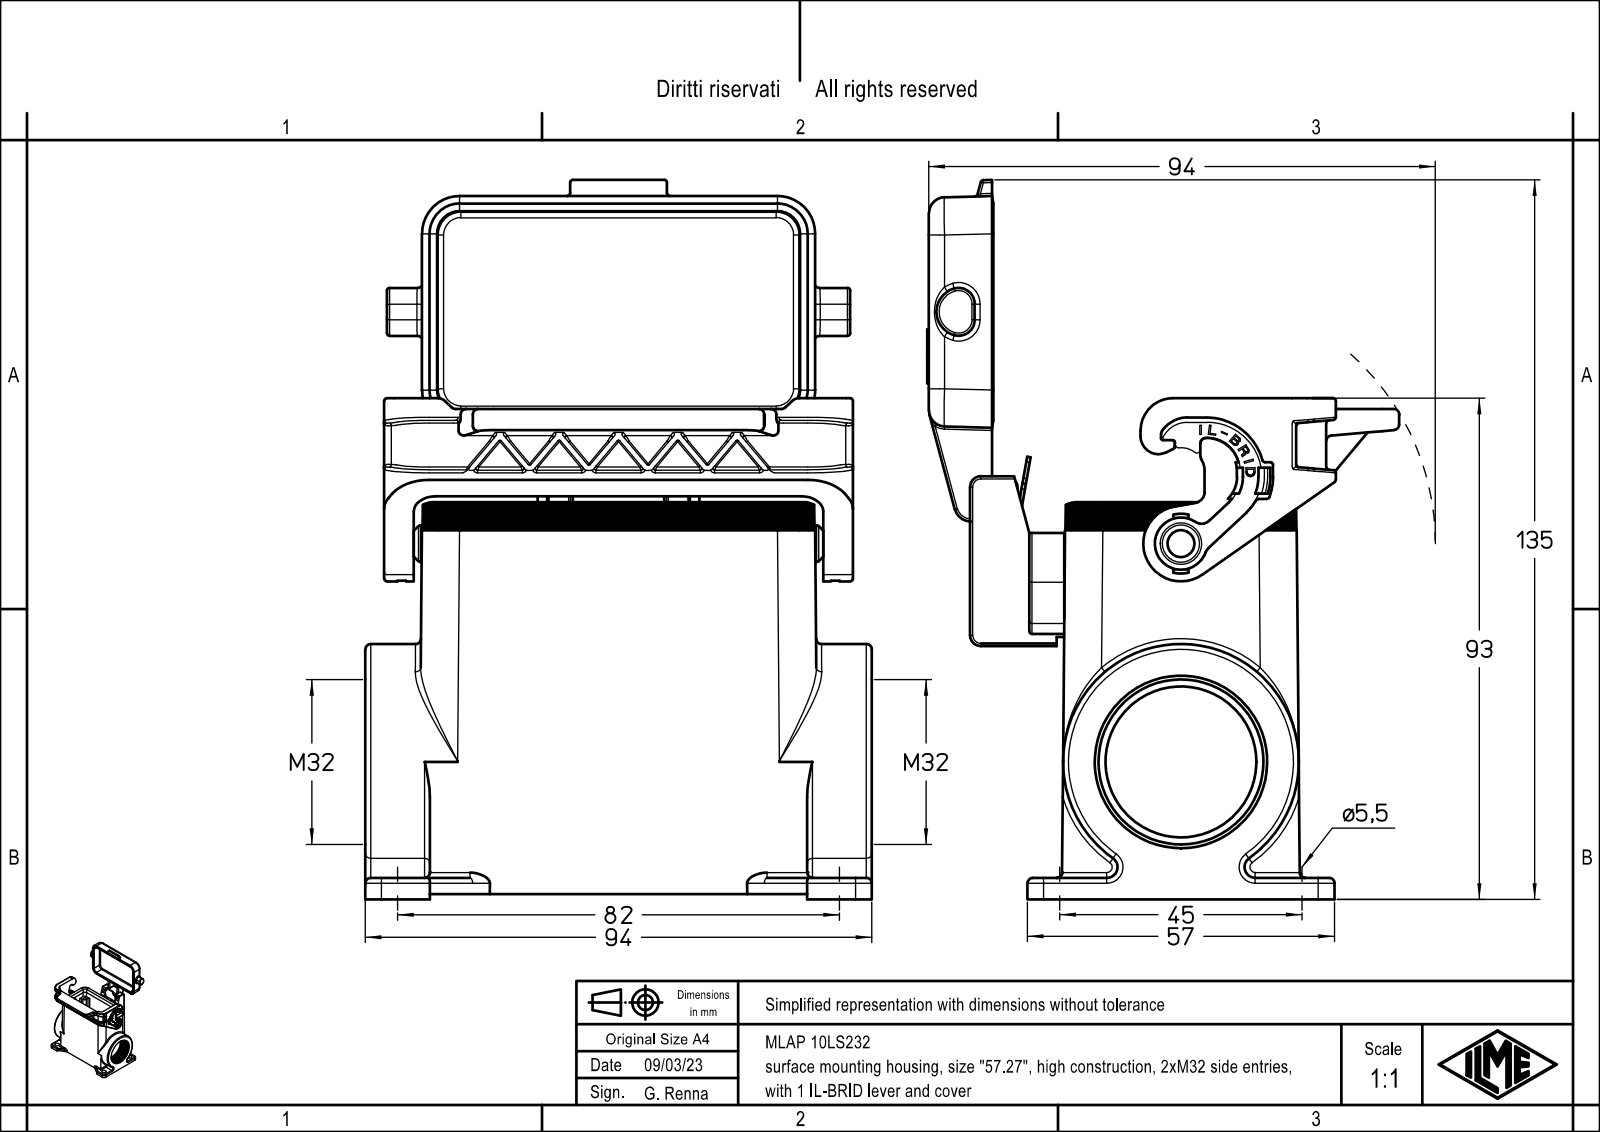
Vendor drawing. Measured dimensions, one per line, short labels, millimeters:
name: MLAP 10LS232
written by: Creo Elements/Direct Modeling 20.1B 02-Apr-2019 (C) Parametric Technology GmbH (AUTOMOTIVE_DESIGN)
unit: mm
bodies: 1 solid, 1402 faces (804 planar, 399 cylindrical, 199 other)
size: 133.49 × 94 × 87.8
volume: 135 244 mm³; area: 72 816 mm²
holes: 4× ⌀3, 4× ⌀3.5, 4× ⌀5.5, 1× ⌀3.25, 1× ⌀5.4, 1× ⌀7.7, 1× ⌀28, 1× ⌀30.6
bosses: 1× ⌀43.75, 1× ⌀8.4, 1× ⌀6.9, 1× ⌀6.8, 1× ⌀5.2, 1× ⌀3.2
rounds: 28× R0.5, 27× R0.1, 23× R0.2, 23× R3, 22× R1, 17× R0.17, 16× R0.33, 15× R2
face distances: 2, 3, 2.8, 87, 1, 4, 69.75, 71.75, 7, 94
hole spacings: 15.4, 38.11, 70.08, 78.27, 27, 45, 57, 63.07
